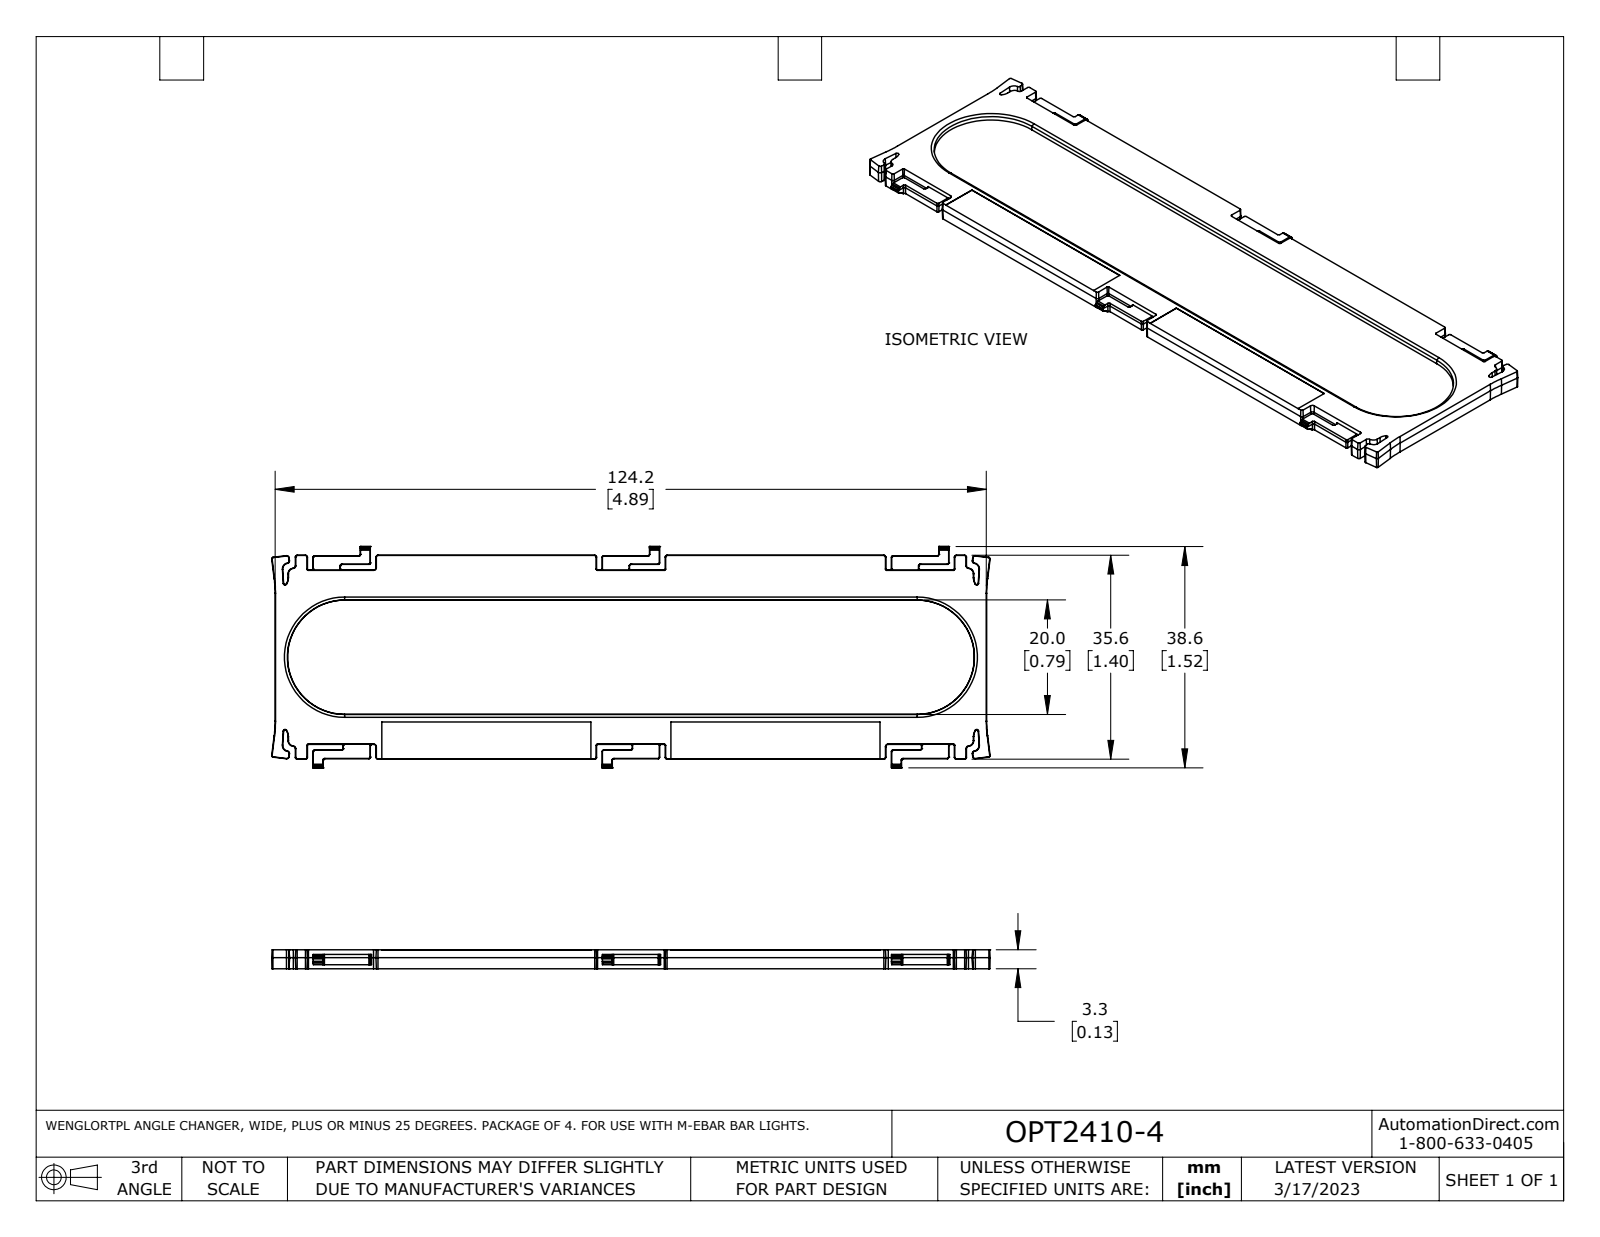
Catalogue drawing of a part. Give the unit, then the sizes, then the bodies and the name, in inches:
Units: inches
Overall size (bounding box): 4.939 × 1.52 × 0.13
Partial cylindrical surfaces — rounded edges, fillets, slot ends (radius × count): R0.006 ×56, R0.02 ×50, R0.079 ×24, R0.01 ×6, R0.098 ×4
Main face-to-face distances: 0.016, 0.026, 0.065, 0.039, 0.055, 0.087, 0.071, 0.061, 0.126, 0.063
Volume: 0.443 in³ · Surface area: 33.01 in²
Bodies: 4 solids, 1142 faces (595 planar, 204 cylindrical, 343 other)
Part name (STEP PRODUCT): OPT2408 Through OPT2417_REV
STEP written by: SolidWorks 2021 (AUTOMOTIVE_DESIGN)
